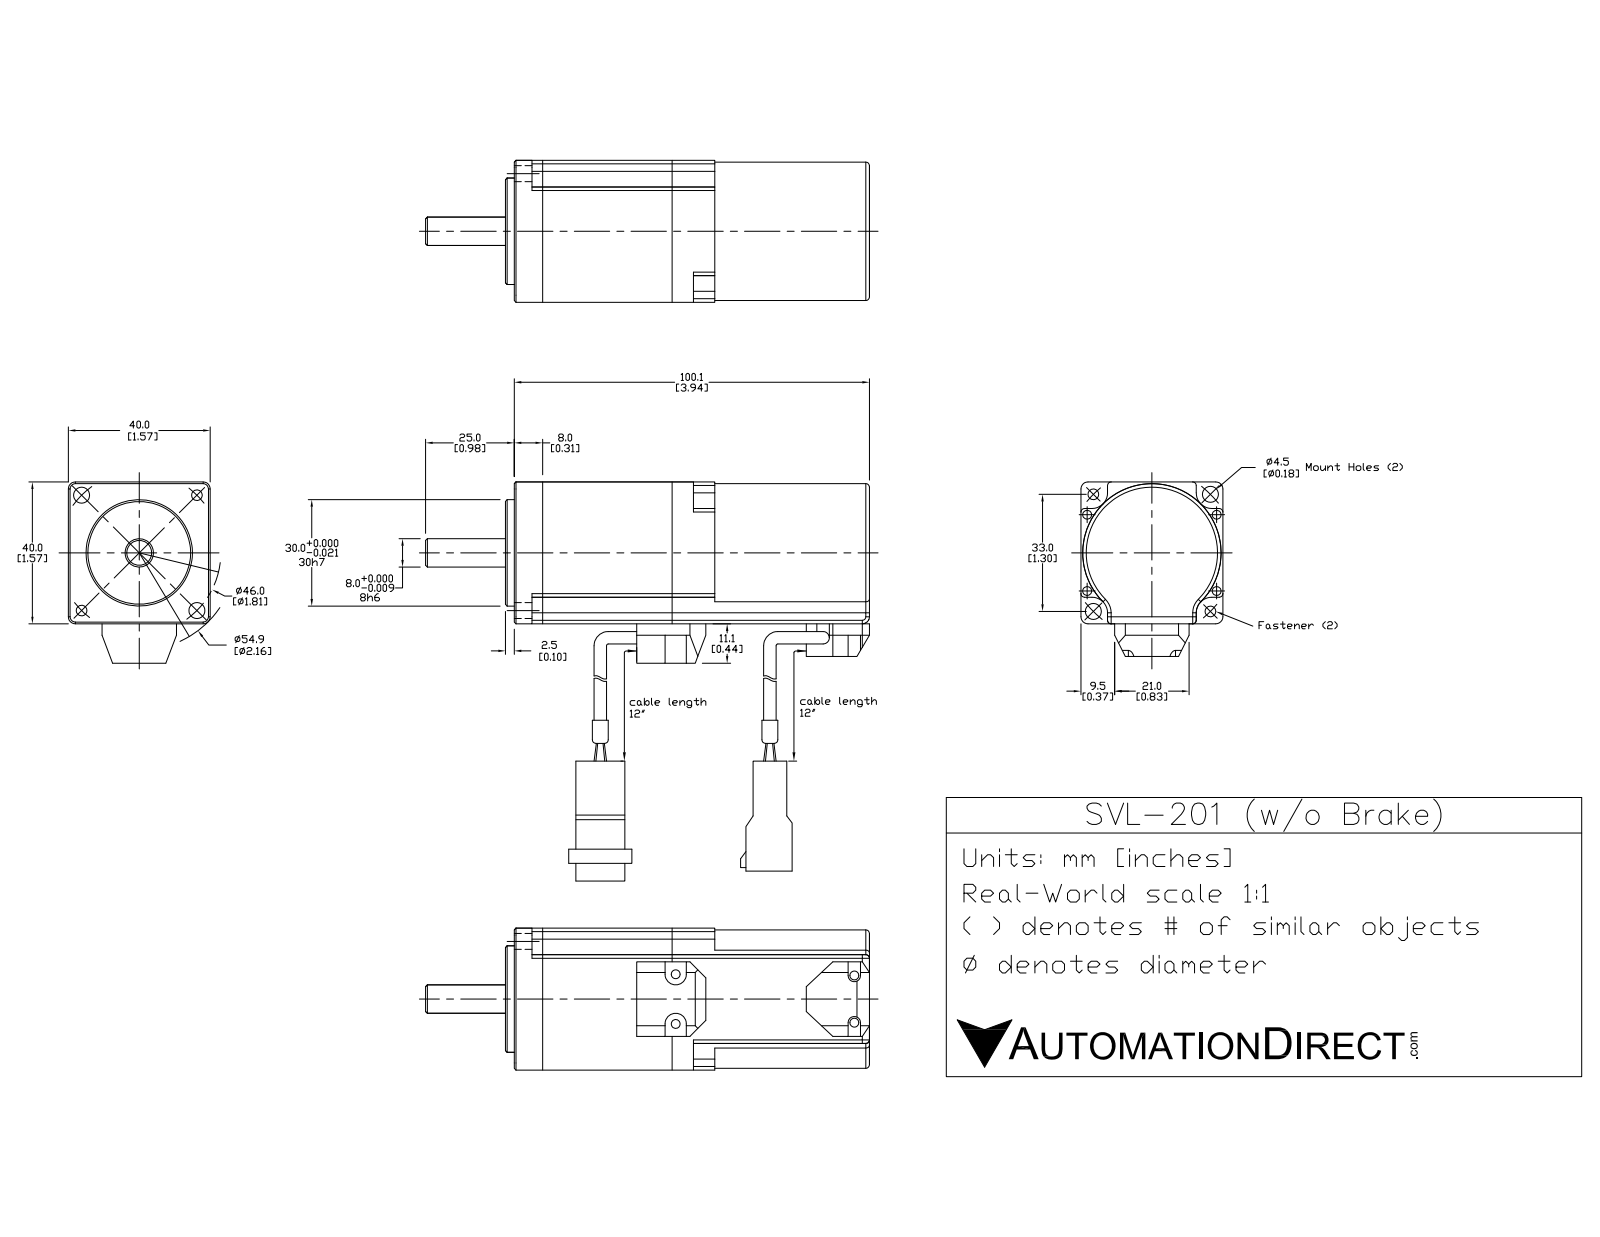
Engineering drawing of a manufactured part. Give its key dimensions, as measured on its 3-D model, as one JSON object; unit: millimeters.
{"part_name": "SVL-201", "step_written_by": "SolidWorks 2015 (AUTOMOTIVE_DESIGN)", "units": "millimeters", "bodies": {"solids": 12, "faces": 296, "planar": 165, "cylindrical": 106, "other": 25}, "overall_size": [125.1, 53.4, 49.76], "volume_mm3": 149410, "surface_area_mm2": 31731, "round_holes": [[2.5, 2], [4.5, 2], [13, 1]], "round_bosses_or_shafts": [[5, 4], [5.5, 3], [30, 1], [8, 1], [7, 1]], "partial_cylinders_radius": [[2, 17], [1, 16], [2.5, 4], [2.75, 4], [4.4, 4], [19.5, 1]], "face_to_face_distances": [40, 36.5, 8.6, 45.1, 55.6, 47, 92.1, 53.1, 100.1, 44.5], "hole_center_spacings": [23, 32.52, 45.99]}
